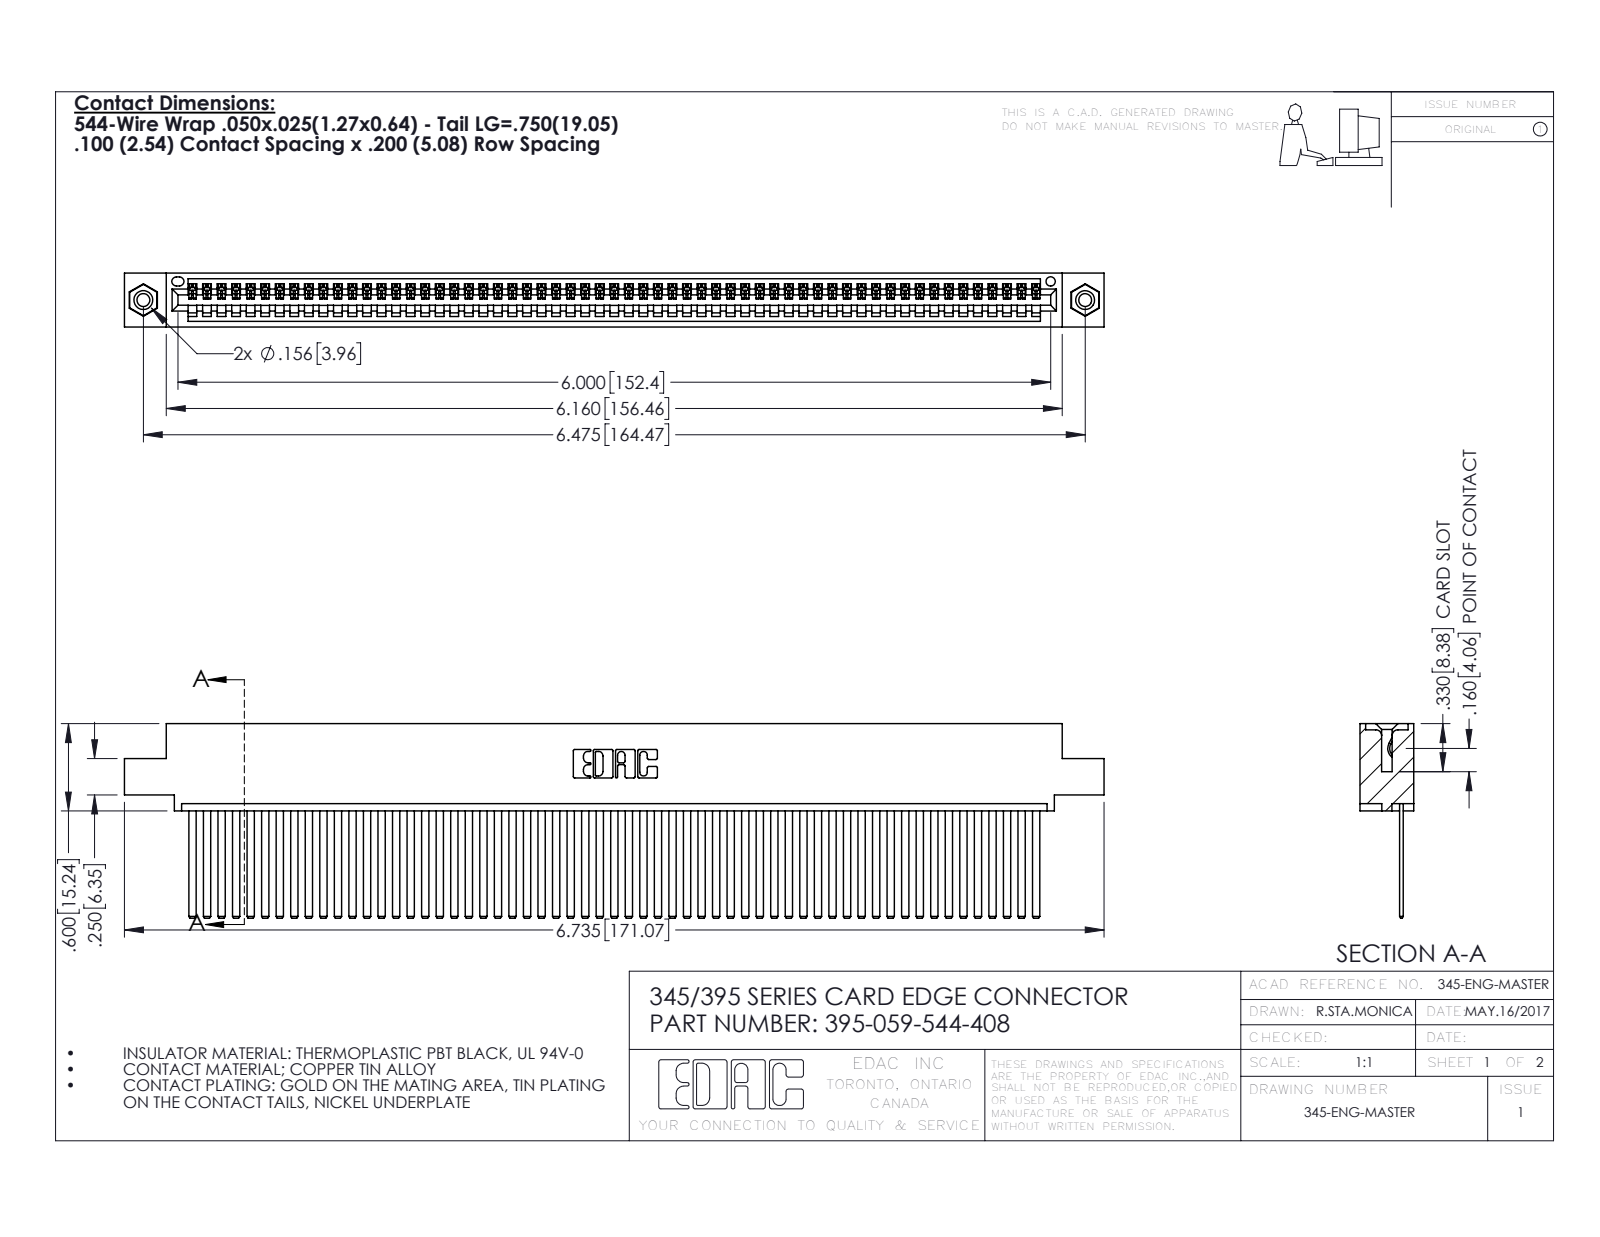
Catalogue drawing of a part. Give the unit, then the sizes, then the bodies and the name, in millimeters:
Units: millimetres
Overall size (bounding box): 171.1 × 34 × 9.4
Round holes (diameter × count): ⌀2.3 ×2, ⌀3.2 ×2, ⌀4 ×2, ⌀1.6 ×1
Round bosses / shafts (diameter × count): ⌀3.9 ×2
Partial cylindrical surfaces — rounded edges, fillets, slot ends (radius × count): R0.2 ×118, R0.3 ×22, R0.2 ×6, R0.8 ×6, R0.7 ×3, R0.8 ×2, R1 ×2, R0.4 ×1
Main face-to-face distances: 1.8, 7.6, 0.6, 2.5, 6.9, 9.4, 5.1, 5.7, 3.8, 1.8
Hole centre spacings: 6.9, 158.5, 164.5
Volume: 16 990 mm³ · Surface area: 24 960 mm²
Bodies: 62 solids, 3258 faces (2240 planar, 1002 cylindrical, 16 other)
Part name (STEP PRODUCT): 345-250-001_345-250-003-102; 395-059-544-408; 345-292-001_345-293-144; 345 Part_0.110 Offset - 0.156 Dia-TI
STEP written by: SolidWorks 2016 (CONFIG_CONTROL_DESIGN)
